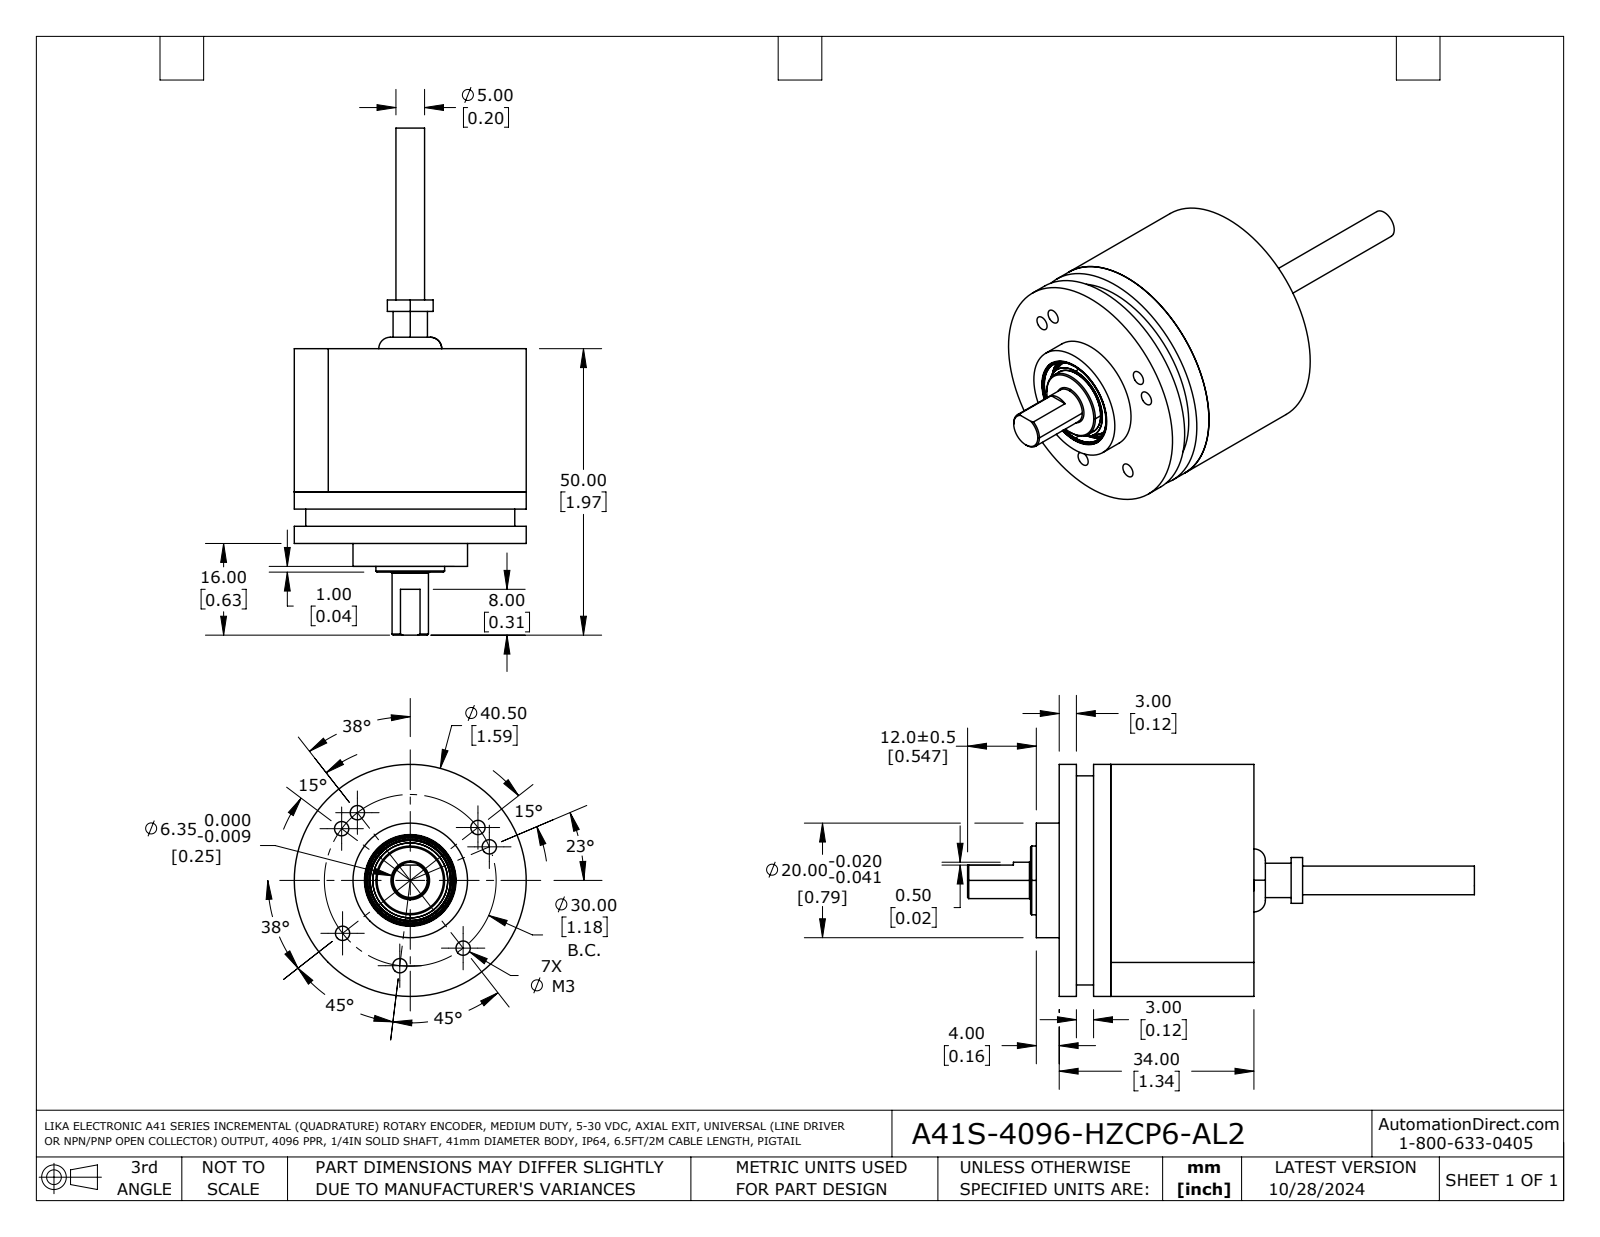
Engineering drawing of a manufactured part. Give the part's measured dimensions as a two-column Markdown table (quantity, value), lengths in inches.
| quantity | value |
| --- | --- |
| part name | A41S-4096-HZCP6-AL2 |
| STEP written by | SolidWorks 2021 (AUTOMOTIVE_DESIGN) |
| units | inches |
| bodies | 11 solids, 422 faces (76 planar, 145 cylindrical, 201 other) |
| overall size | 3.484 × 1.594 × 1.594 |
| volume | 1.175 in³ |
| surface area | 28.29 in² |
| round holes (diameter × count) | 0.063 × 7, 0.098 × 7, 0.157 × 3, 0.087 × 2, 0.169 × 1, 0.295 × 1, 0.512 × 1, 0.602 × 1, 0.612 × 1, 0.63 × 1, 1.516 × 1 |
| round bosses / shafts (diameter × count) | 0.079 × 2, 1.594 × 1, 1.496 × 1, 1.457 × 1, 1.437 × 1, 0.787 × 1, 0.472 × 1, 0.315 × 1 |
| partial cylindrical surfaces (radius × count) | 0.039 × 14, 0.007 × 6, 0.008 × 2 |
| main face-to-face distances | 0.118, 1.339, 0.433, 0.906, 1.22, 0.079, 0.866, 0.984, 0.787, 0.039 |
| hole center spacings | 0.591, 0.669, 0.835, 0.11, 0.118, 0.837, 0.945, 1.257 |
